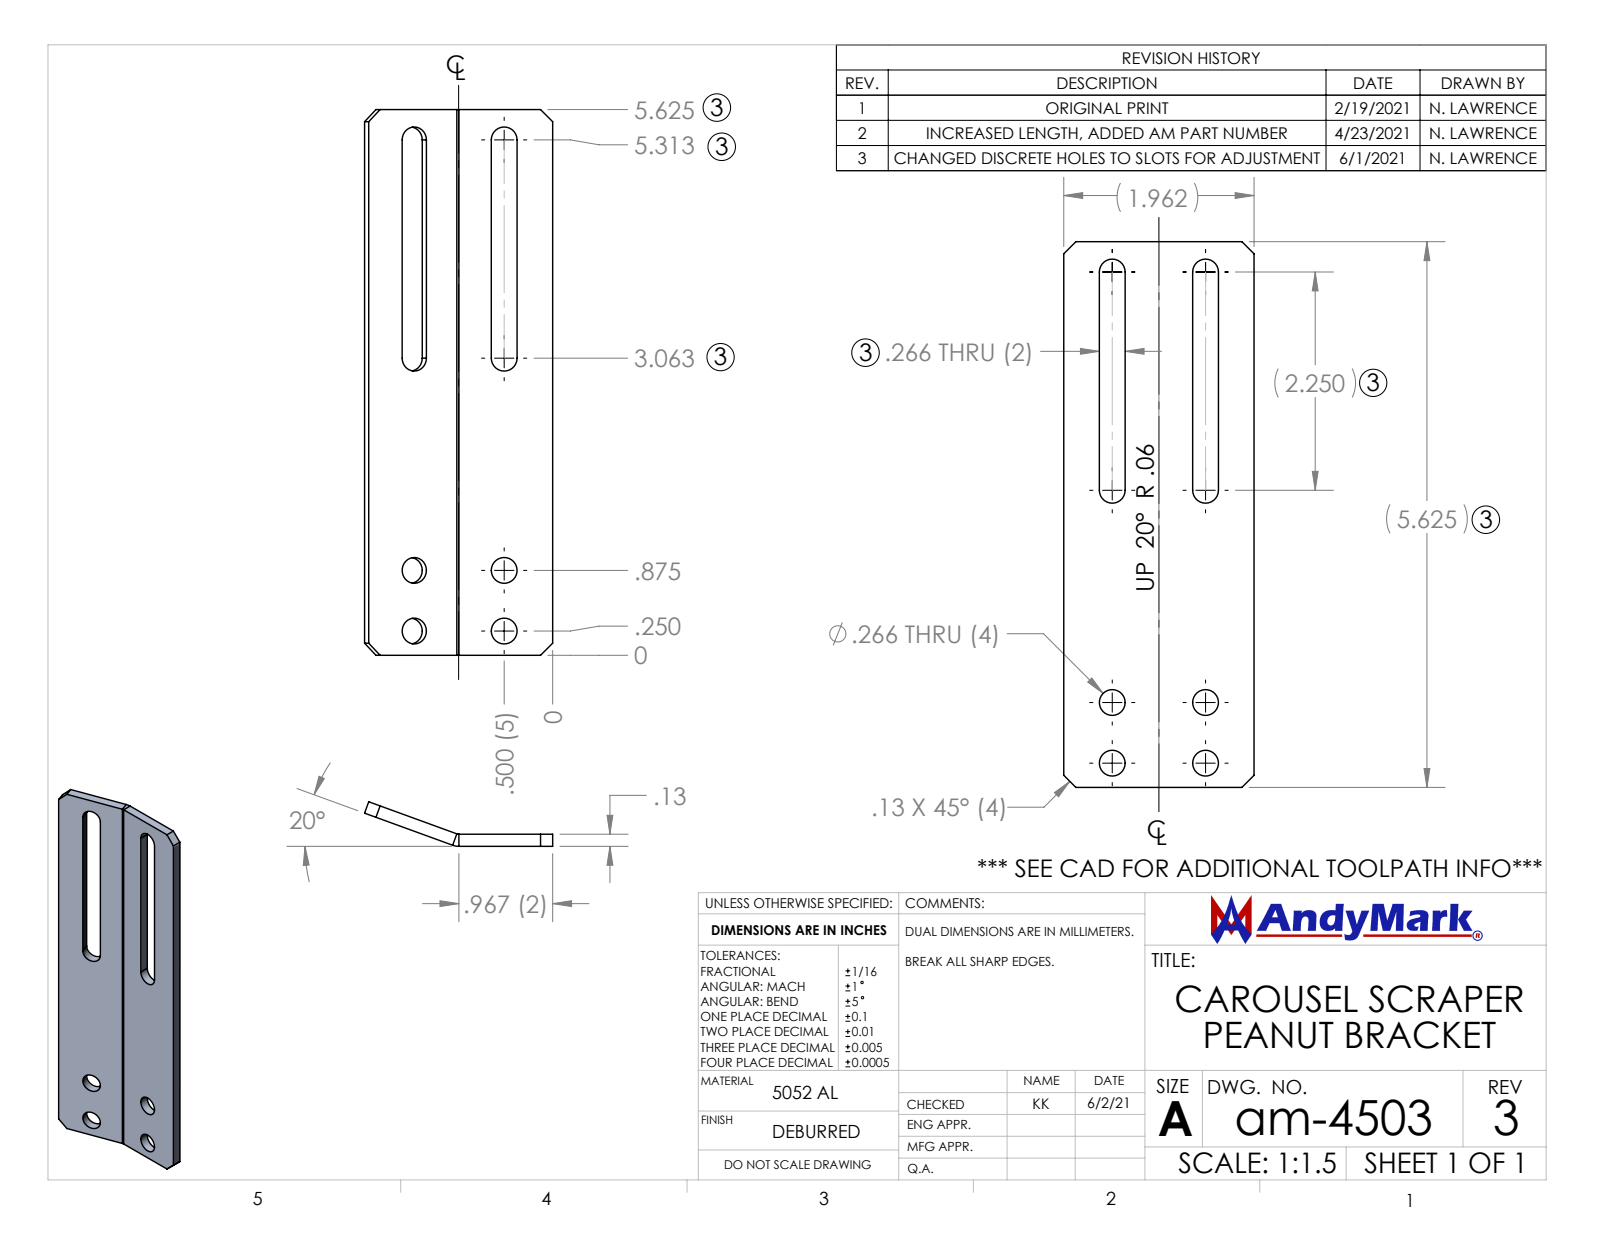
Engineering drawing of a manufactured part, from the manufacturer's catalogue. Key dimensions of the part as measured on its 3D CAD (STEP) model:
Part name (STEP PRODUCT): am-4503 Carousel Scraper Peanut Bracket
STEP written by: SolidWorks 2019 (AUTOMOTIVE_DESIGN)
Units: inches
Bodies: 1 solid, 30 faces (20 planar, 10 cylindrical, 0 other)
Overall size (bounding box): 5.625 × 1.94 × 0.459
Volume: 1.195 in³ · Surface area: 22.74 in²
Round holes (diameter × count): ⌀0.266 ×4
Partial cylindrical surfaces — rounded edges, fillets, slot ends (radius × count): R0.133 ×4, R0.062 ×1, R0.187 ×1
Main face-to-face distances: 0.125, 0.125, 0.633, 0.266, 0.367, 5.625
Hole centre spacings: 0.625
